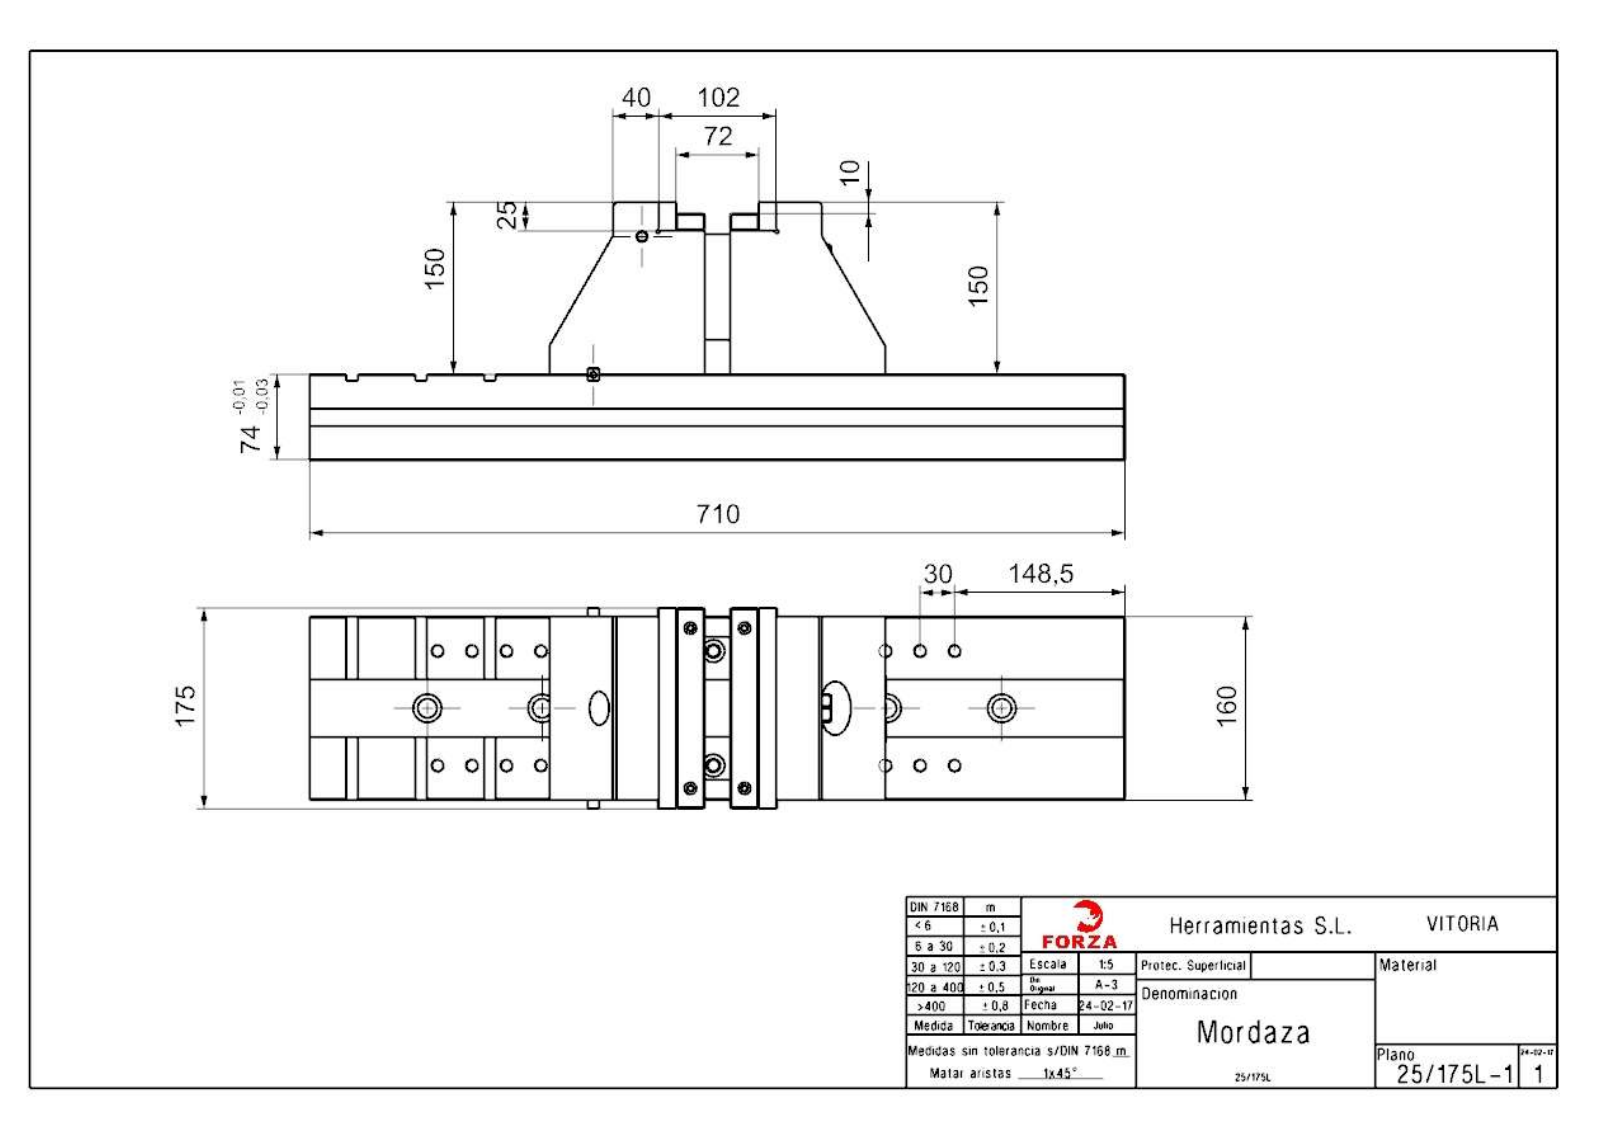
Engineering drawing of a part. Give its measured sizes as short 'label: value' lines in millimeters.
name: 25_175L_Mordaza
written by: SIEMENS PLM Software NX 9.0 (CONFIG_CONTROL_DESIGN)
unit: mm
bodies: 30 solids, 666 faces (387 planar, 168 cylindrical, 111 other)
size: 710 × 225 × 175
volume: 12 040 000 mm³; area: 984 381 mm²
holes: 40× ⌀10.3, 16× ⌀12.5, 12× ⌀19, 6× ⌀20, 5× ⌀5, 5× ⌀16, 4× ⌀6.5, 4× ⌀10.5, 4× ⌀11, 4× ⌀17, 4× ⌀25, 3× ⌀8.5
bosses: 2× ⌀47, 1× ⌀44, 1× ⌀42, 1× ⌀33.8, 1× ⌀29.74, 1× ⌀26.5, 1× ⌀26, 1× ⌀24.7
rounds: 2× R2, 2× R4, 2× R5, 2× R5.5
face distances: 75, 160, 43.5, 31.5, 55, 45, 25, 115, 42.5, 1
hole spacings: 100, 61.5, 69.33, 30, 32, 38, 49.68, 123
